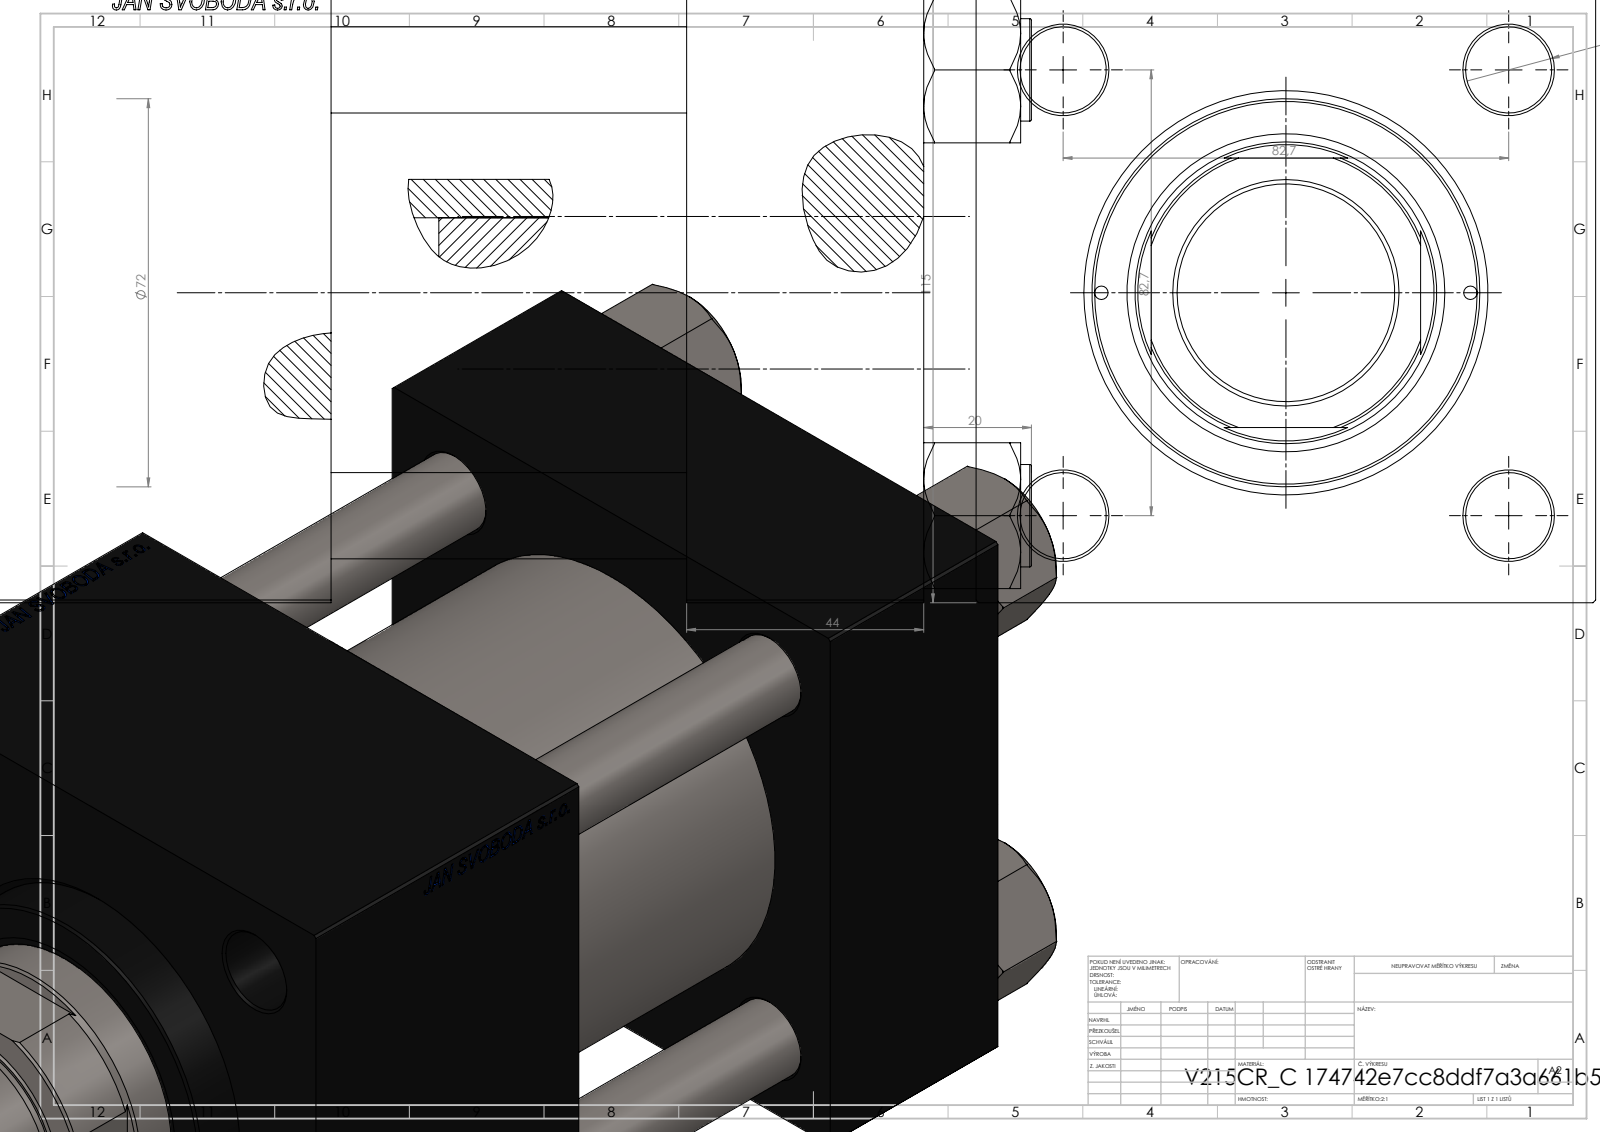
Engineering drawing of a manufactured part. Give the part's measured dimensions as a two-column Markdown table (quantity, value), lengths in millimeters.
| quantity | value |
| --- | --- |
| part name | V215CR_VCP_C; NUT_M5_C; ROD_END_AH; V215_VC_A (+2 more) |
| STEP written by | SolidWorks 2019 (CONFIG_CONTROL_DESIGN) |
| units | millimeters |
| bodies | 12 solids, 1213 faces (579 planar, 92 cylindrical, 542 other) |
| overall size | 286 × 115 × 115 |
| volume | 1 939 000 mm³ |
| surface area | 290 711 mm² |
| round holes (diameter × count) | 16 × 4, 2.5 × 2, 7 × 2, 26.44 × 2, 35 × 2, 40.5 × 1, 56 × 1, 59 × 1, 61 × 1, 72 × 1, 80 × 1 |
| round bosses / shafts (diameter × count) | 19 × 4, 86 × 1, 42 × 1, 40 × 1 |
| partial cylindrical surfaces (radius × count) | 27 × 1 |
| main face-to-face distances | 115, 44, 110, 66, 179, 135, 69, 20, 56, 87 |
| hole center spacings | 41.96, 58.48, 82.7, 86.17, 34.25, 116.96, 68.5, 111 |
